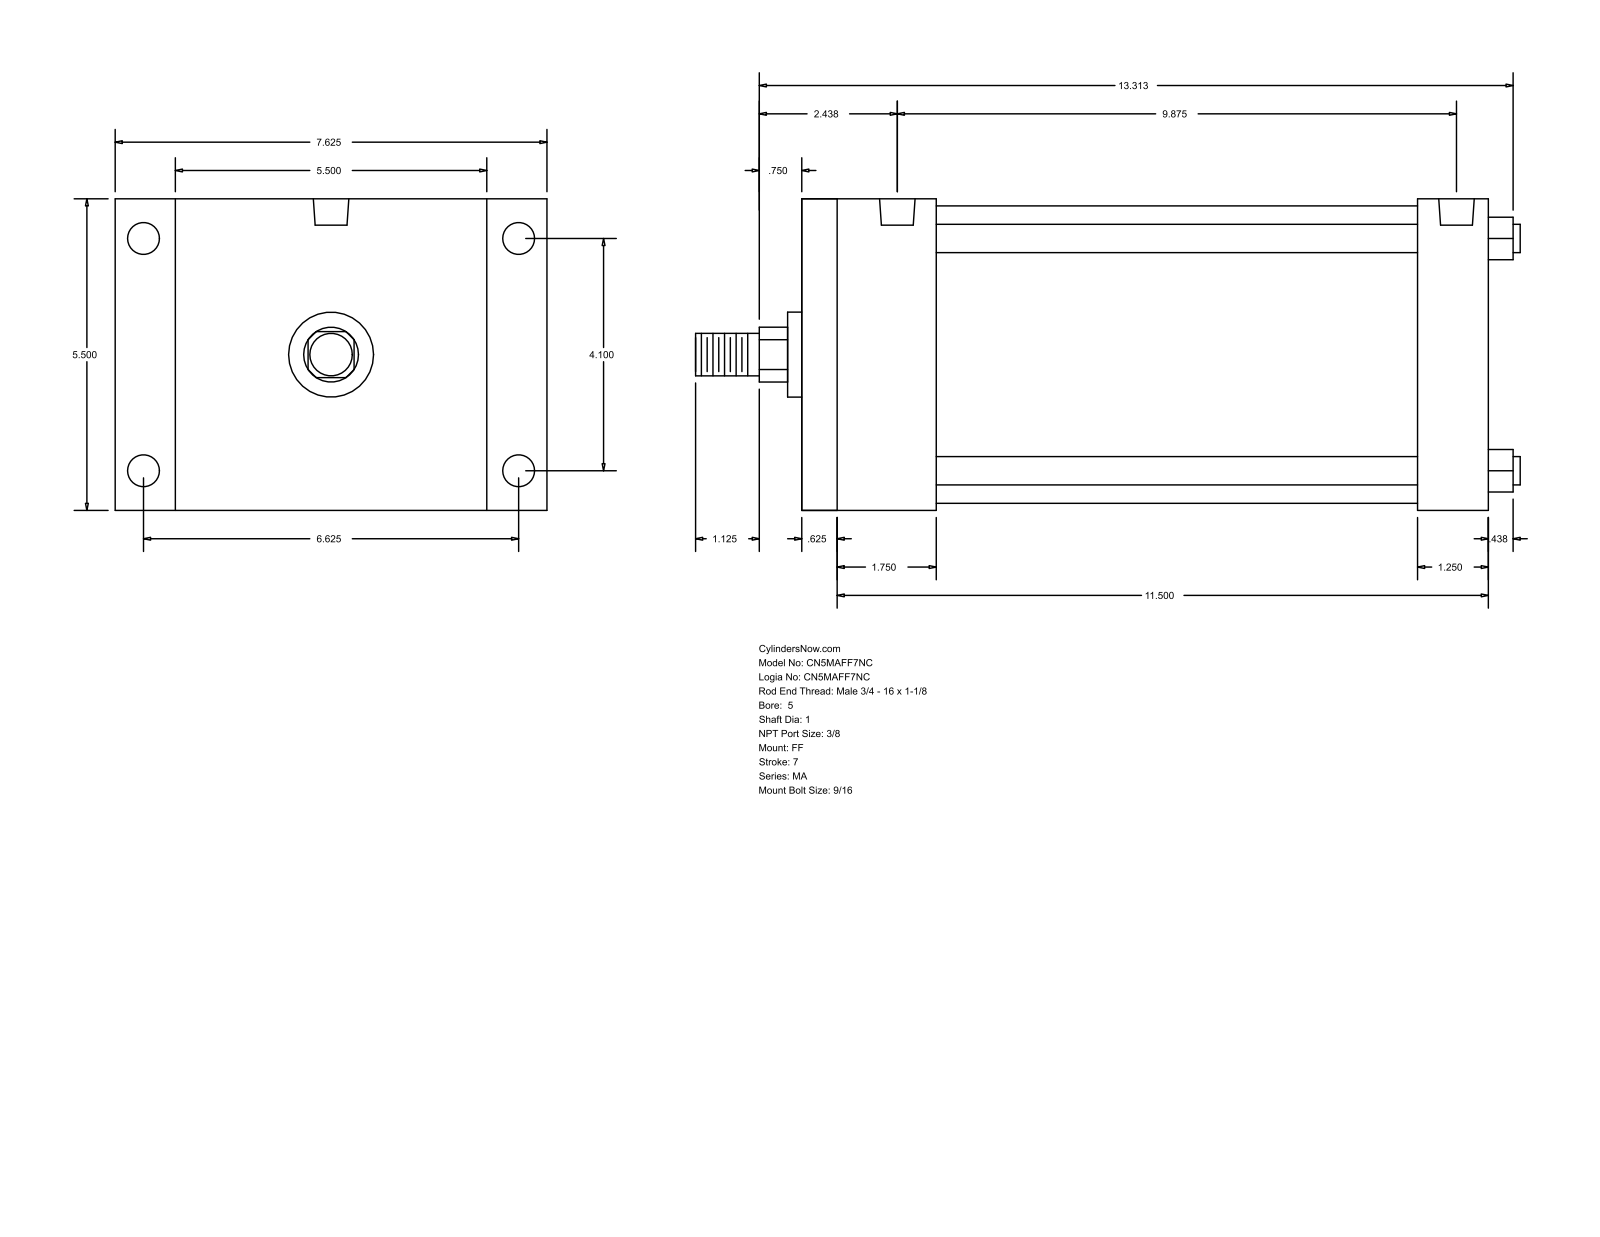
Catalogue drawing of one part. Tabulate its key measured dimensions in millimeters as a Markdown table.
| quantity | value |
| --- | --- |
| part name | MA_FF__0500_1 |
| STEP written by | GSSL Pune (CONFIG_CONTROL_DESIGN) |
| units | millimeters |
| bodies | 0 solids, 92 faces (64 planar, 28 cylindrical, 0 other) |
| overall size | 369.89 × 193.68 × 139.7 |
| round holes (diameter × count) | 11.11 × 4, 14.29 × 4, 15.93 × 2 |
| round bosses / shafts (diameter × count) | 12.7 × 4, 133.35 × 1, 38.1 × 1, 25.4 × 1, 19.05 × 1 |
| partial cylindrical surfaces (radius × count) | 12.29 × 1 |
| main face-to-face distances | 139.7, 307.97, 15.87, 292.1, 276.22, 260.35, 31.75, 60.33, 44.46, 215.89 |
| hole center spacings | 4.76, 104.14, 168.28, 197.9, 241.31, 246.07, 250.83 |
